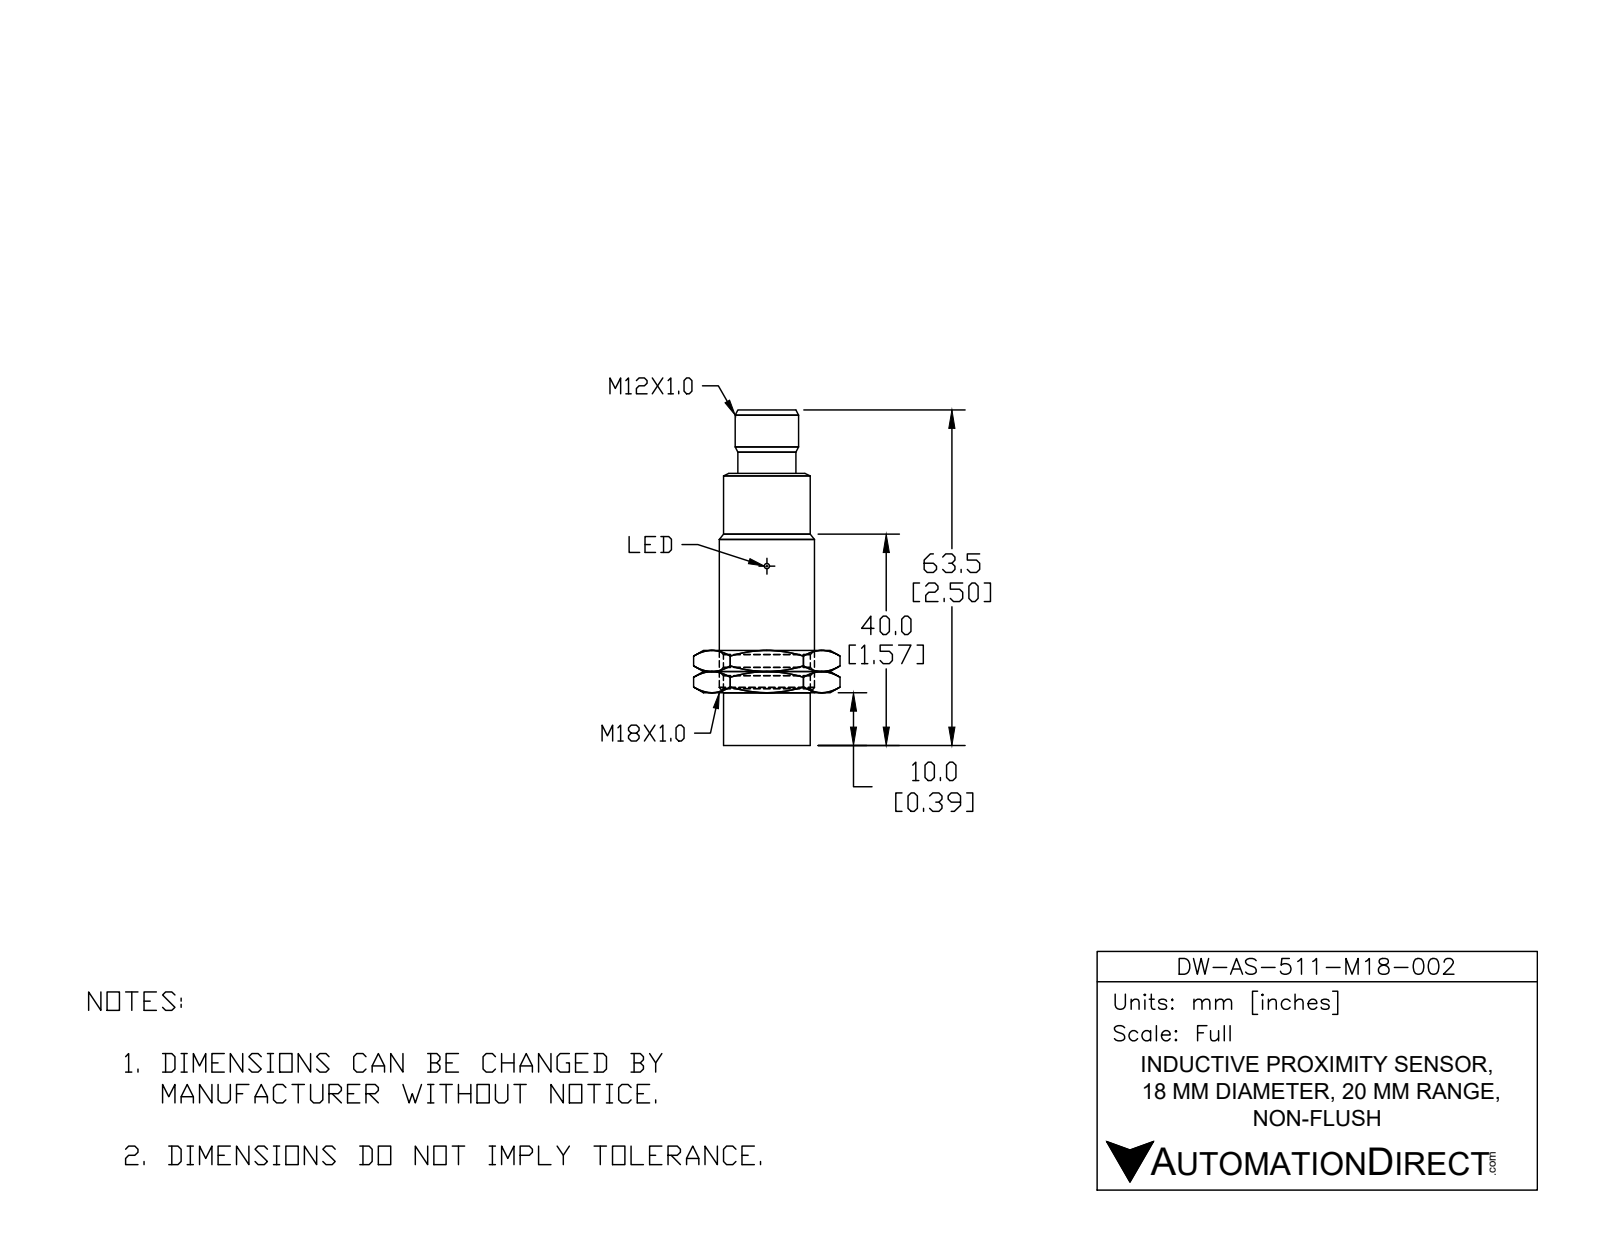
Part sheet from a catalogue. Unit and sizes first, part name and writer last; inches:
Units: inches
Overall size (bounding box): 2.502 × 0.709 × 0.709
Round holes (diameter × count): ⌀0.12 ×2, ⌀0.335 ×1
Round bosses / shafts (diameter × count): ⌀0.043 ×3, ⌀0.709 ×1, ⌀0.65 ×1, ⌀0.646 ×1, ⌀0.472 ×1, ⌀0.415 ×1
Partial cylindrical surfaces — rounded edges, fillets, slot ends (radius × count): R0.019 ×2, R0.022 ×1
Main face-to-face distances: 1.988, 2.159, 0.171, 2.502, 0.514, 0.343, 1.654, 0.335, 0.506, 0.848
Volume: 0.779 in³ · Surface area: 6.427 in²
Bodies: 1 solid, 36 faces (13 planar, 14 cylindrical, 9 other)
Part name (STEP PRODUCT): DW-AS-511-M18-002
STEP written by: SolidWorks 2017 (AUTOMOTIVE_DESIGN)
